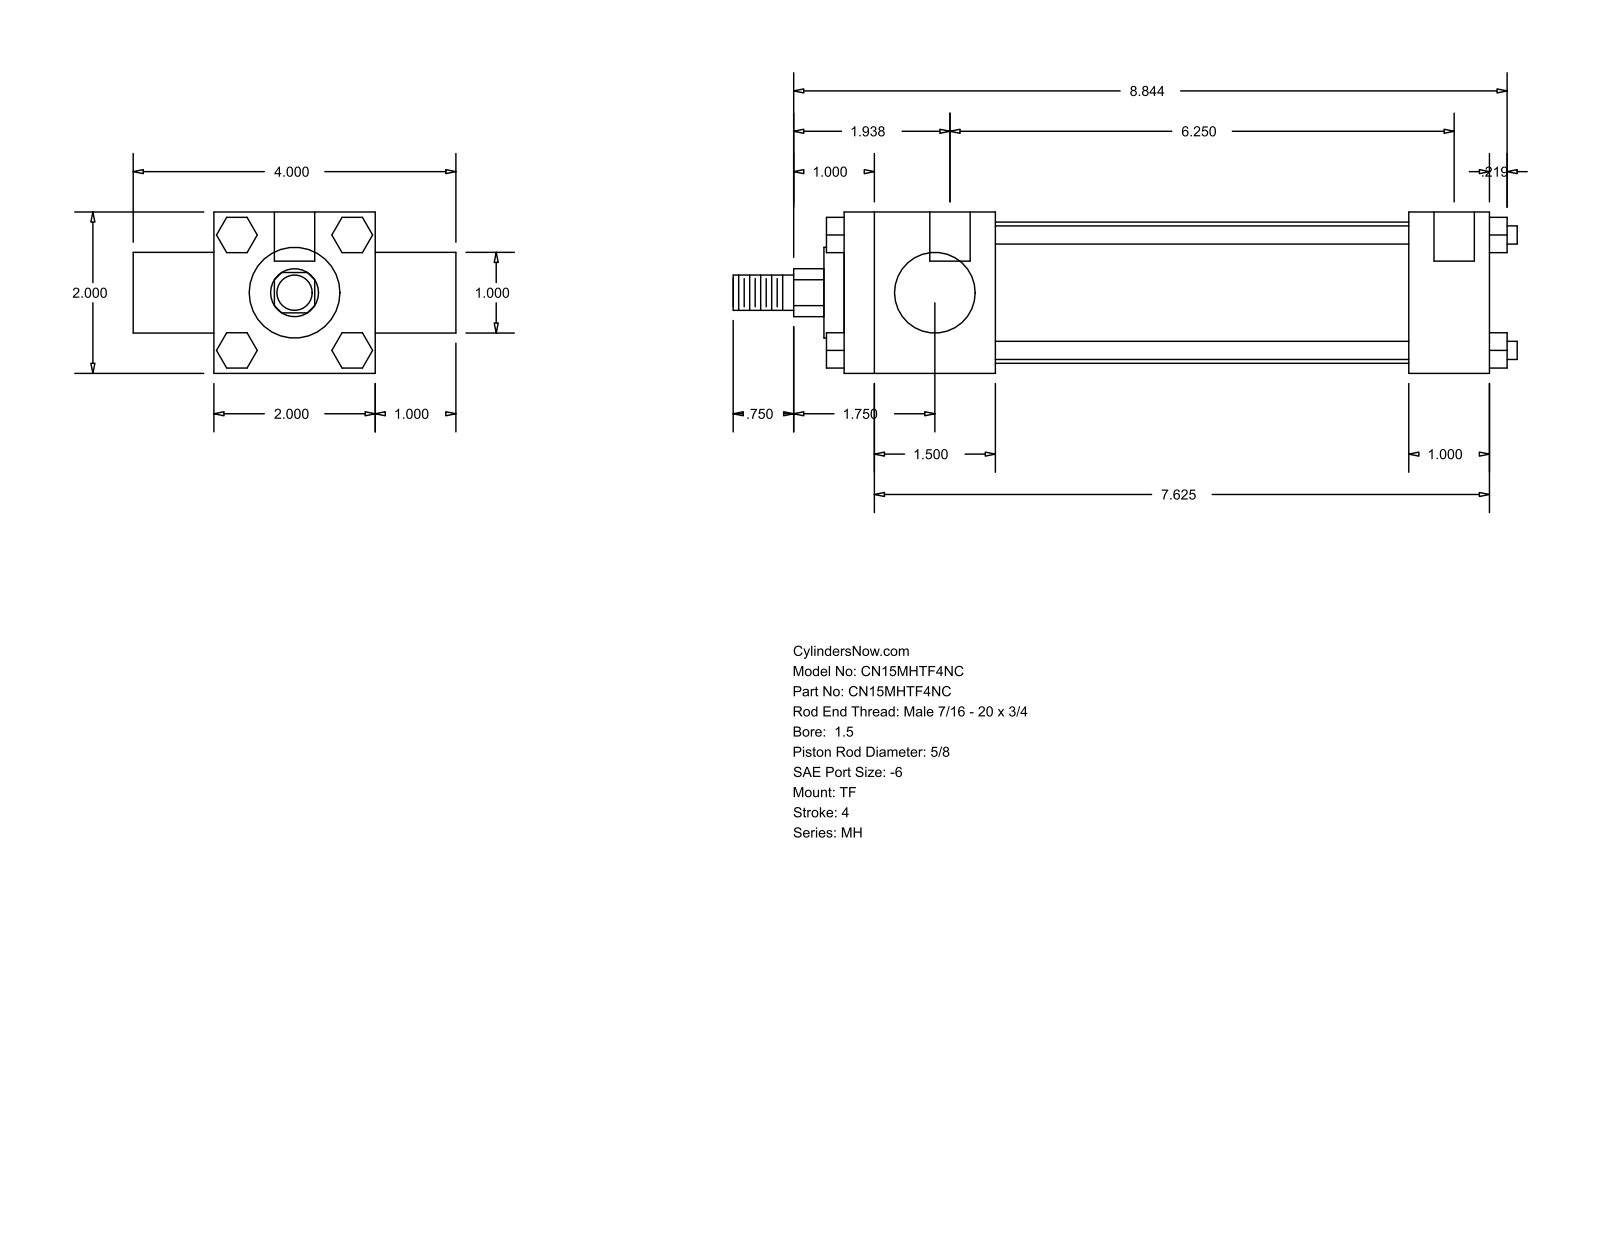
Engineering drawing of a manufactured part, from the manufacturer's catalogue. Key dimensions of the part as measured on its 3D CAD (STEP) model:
Part name (STEP PRODUCT): MH_TF__0150_0.625
STEP written by: GSSL Pune (CONFIG_CONTROL_DESIGN)
Units: millimetres
Bodies: 0 solids, 120 faces (92 planar, 28 cylindrical, 0 other)
Overall size (bounding box): 246.86 × 101.6 × 50.8
Round holes (diameter × count): ⌀5.56 ×3, ⌀12.7 ×2
Round bosses / shafts (diameter × count): ⌀5.71 ×4, ⌀44.45 ×1, ⌀28.57 ×1, ⌀25.4 ×1, ⌀15.88 ×1, ⌀11.11 ×1
Partial cylindrical surfaces — rounded edges, fillets, slot ends (radius × count): R7.54 ×1
Main face-to-face distances: 50.8, 203.19, 25.4, 76.2, 47.62, 155.57, 177.8, 130.18, 25.39, 5.56
Hole centre spacings: 3.17, 158.75, 161.92
